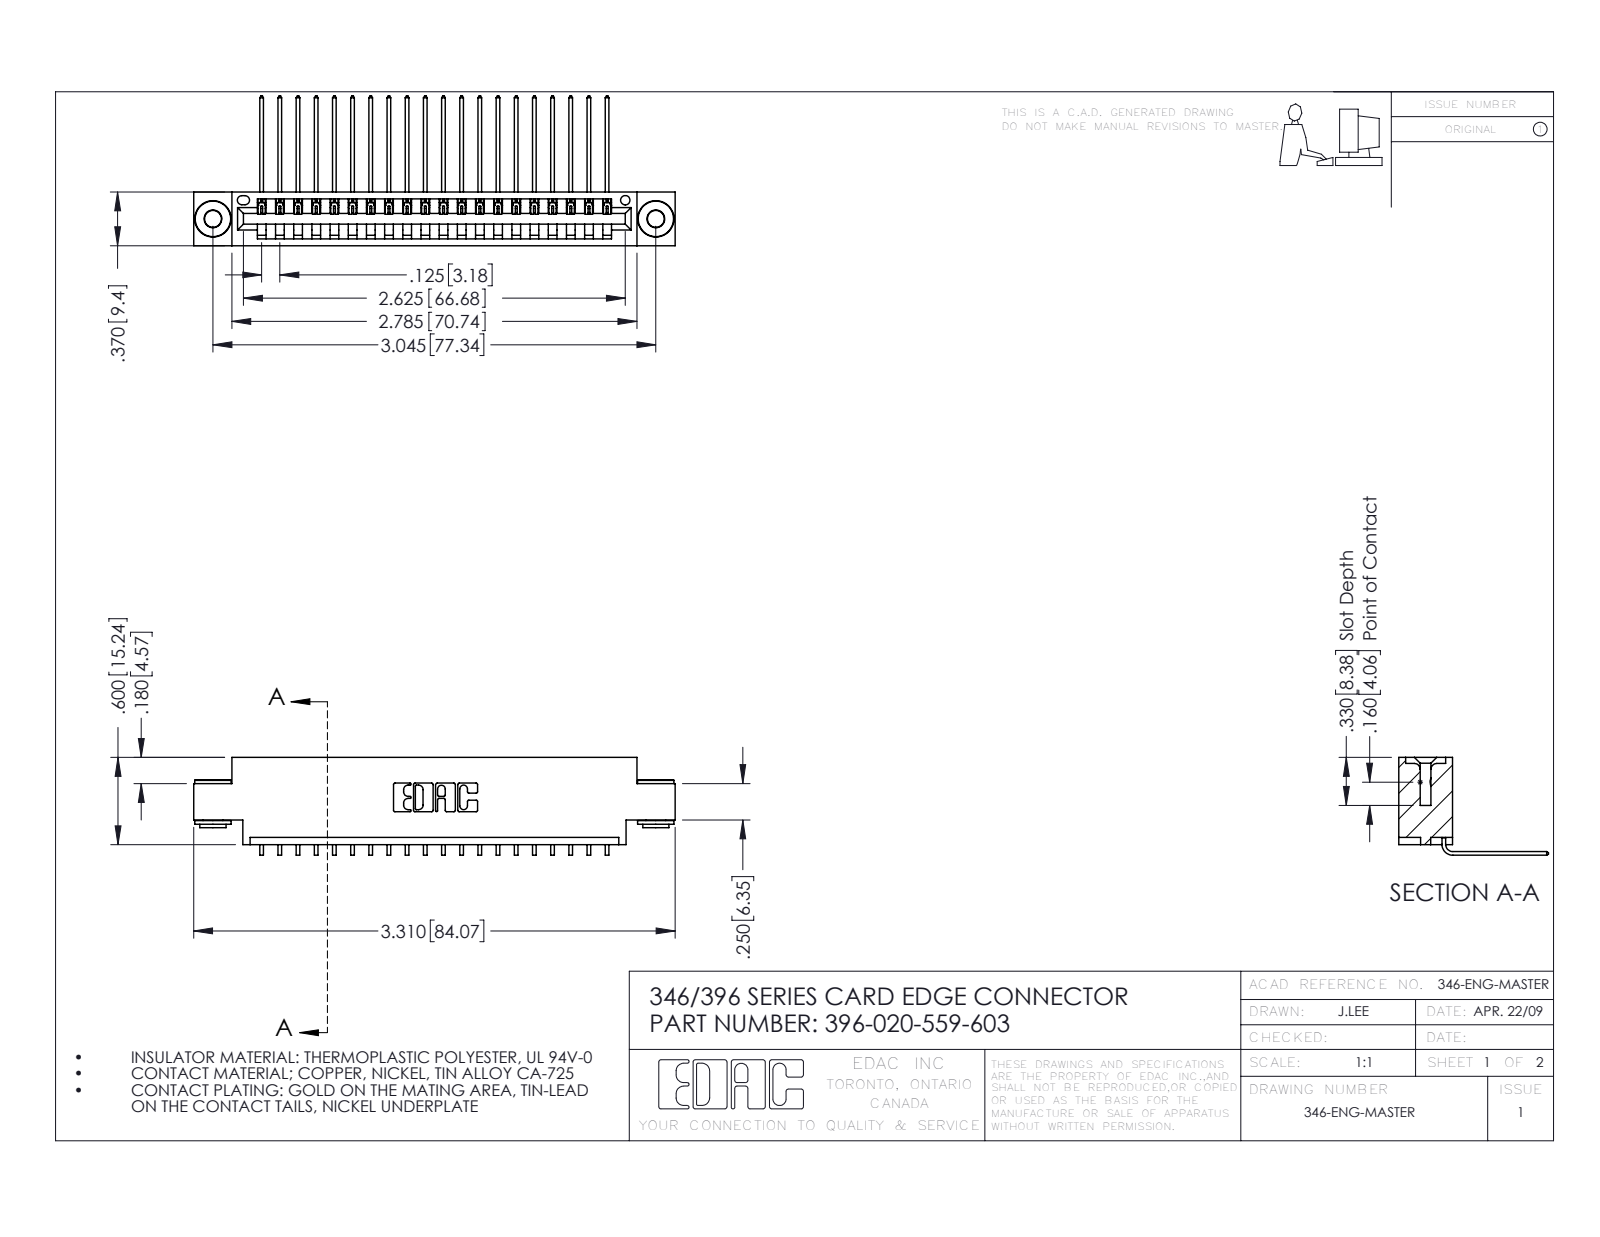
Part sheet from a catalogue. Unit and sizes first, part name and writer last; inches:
Units: inches
Overall size (bounding box): 3.31 × 1.03 × 0.673
Round holes (diameter × count): ⌀0.116 ×2, ⌀0.156 ×2, ⌀0.064 ×1
Round bosses / shafts (diameter × count): ⌀0.25 ×2, ⌀0.18 ×2, ⌀0.136 ×2
Partial cylindrical surfaces — rounded edges, fillets, slot ends (radius × count): R0.006 ×40, R0.01 ×22, R0.007 ×6, R0.031 ×6, R0.026 ×3, R0.031 ×2, R0.04 ×2, R0.014 ×1
Main face-to-face distances: 0.048, 0.37, 0.322, 0.25, 0.025, 0.072, 0.148, 0.222, 0.1, 0.174
Hole centre spacings: 0.246, 2.837, 3.045
Volume: 0.478 in³ · Surface area: 16 in²
Bodies: 23 solids, 1364 faces (930 planar, 426 cylindrical, 8 other)
Part name (STEP PRODUCT): 346 Part_0.170 Offset - 0.156 Dia-TH; 345-250-002_345-250-002-102; 396-020-559-603; 345-292-001_558 559 Tail - 1
STEP written by: SolidWorks 2016 (CONFIG_CONTROL_DESIGN)
